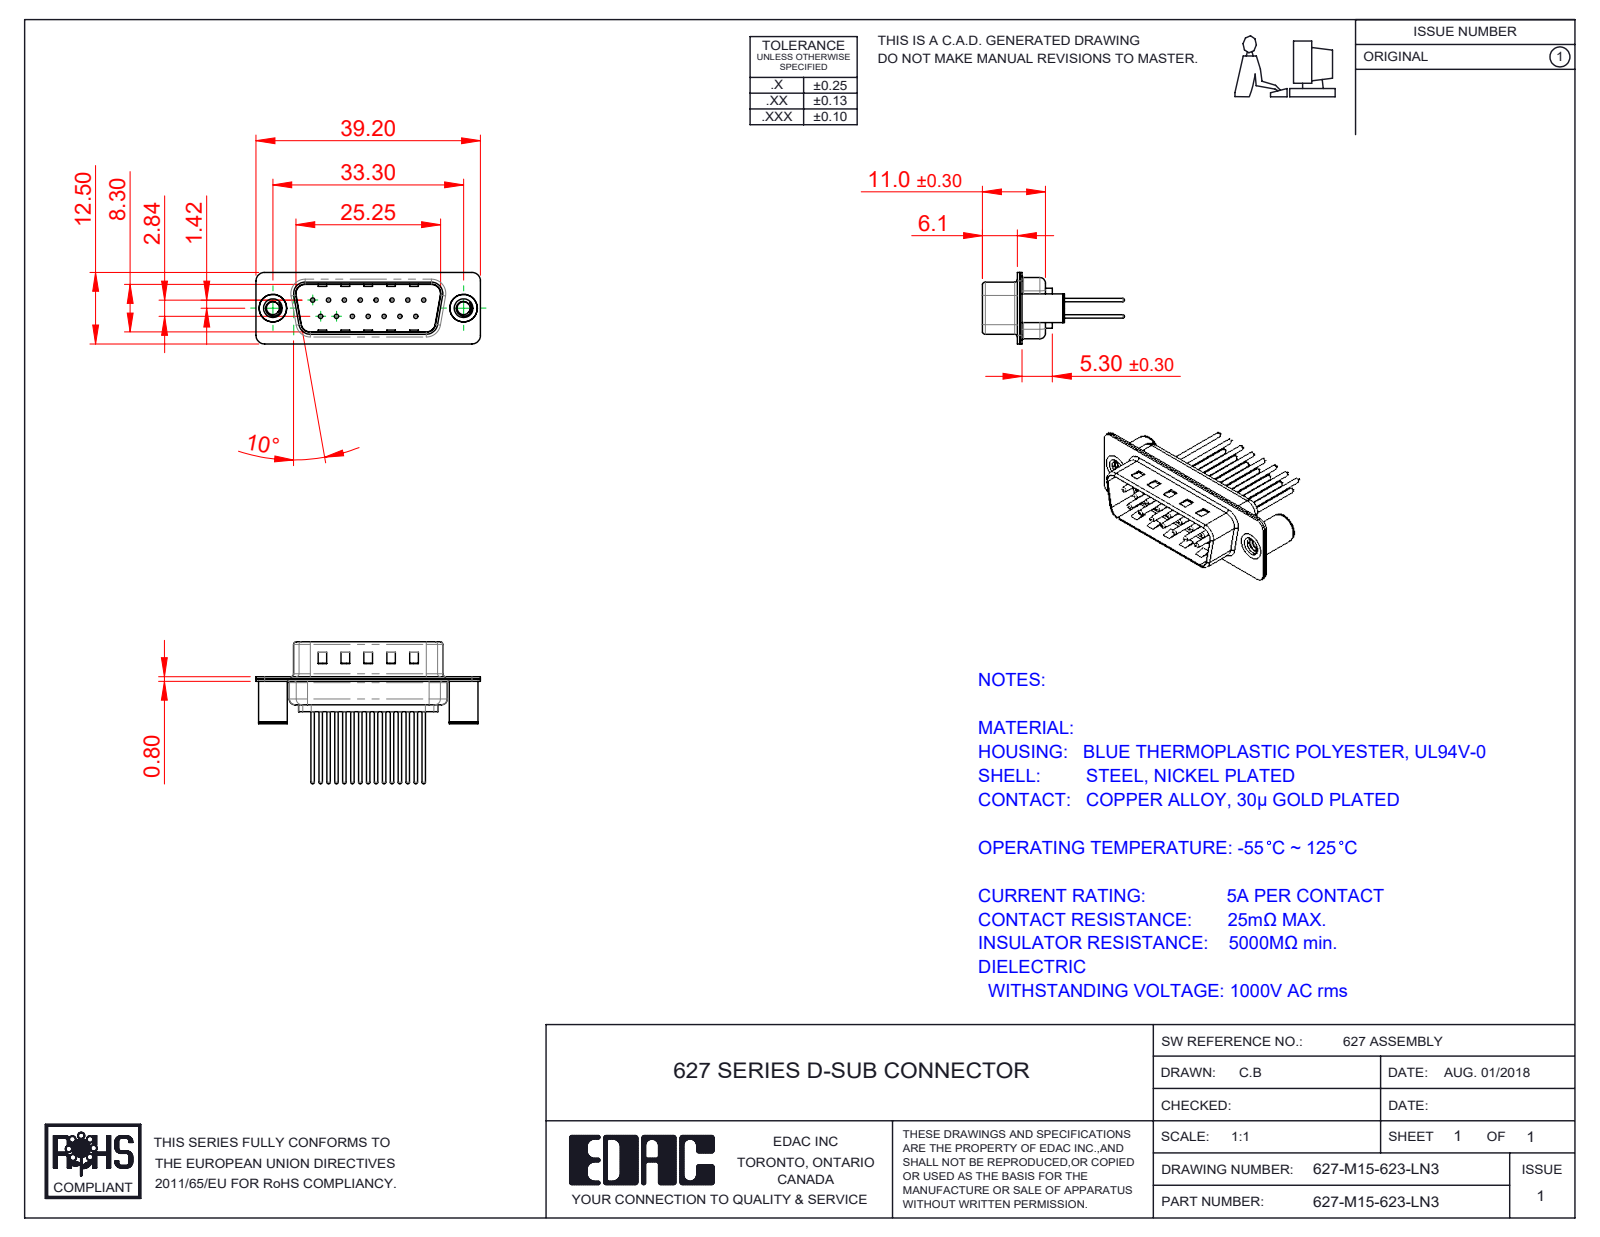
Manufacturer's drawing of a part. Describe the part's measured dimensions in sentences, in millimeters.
The part is named "627M Shell Rear_15 Contacts; 627M Shell Front_15 Contacts; 627M 4-40 Threaded Board Spacer; 627M Contact Row 1_23 (+3 more)". Its 3-D file was written by "SolidWorks 2020 (CONFIG_CONTROL_DESIGN)". It is 20 solids with 929 faces: 244 planar, 367 cylindrical and 318 other. Overall it measures 39.2 by 24.77 by 12.5 millimeters. Its volume is 1 995 cubic millimeters and its surface area 5 261 square millimeters. Round holes: 15 of diameter 0.75, 15 of diameter 1.6, 15 of diameter 2, 2 of diameter 2.26, 2 of diameter 3.26, 2 of diameter 4, 2 of diameter 4.8. Round bosses or shafts: 15 of diameter 1.5, 15 of diameter 0.6, 2 of diameter 5, 2 of diameter 4.9. Partial cylindrical surfaces (rounded edges, fillets, slot ends): 16 of radius 1.5, 12 of radius 2, 8 of radius 0.5, 8 of radius 1.6, 4 of radius 0.25, 4 of radius 0.6, 4 of radius 0.65, 4 of radius 0.9. The main face-to-face distances are 0.4, 0.8, 9.5, 9.1, 8.7, 9.9, 1.2, 5.3, 6.1, 5.7. The hole center spacings are 3.16, 2.77, 5.54, 8.31, 11.08, 5.03, 5.04, 7.48.
